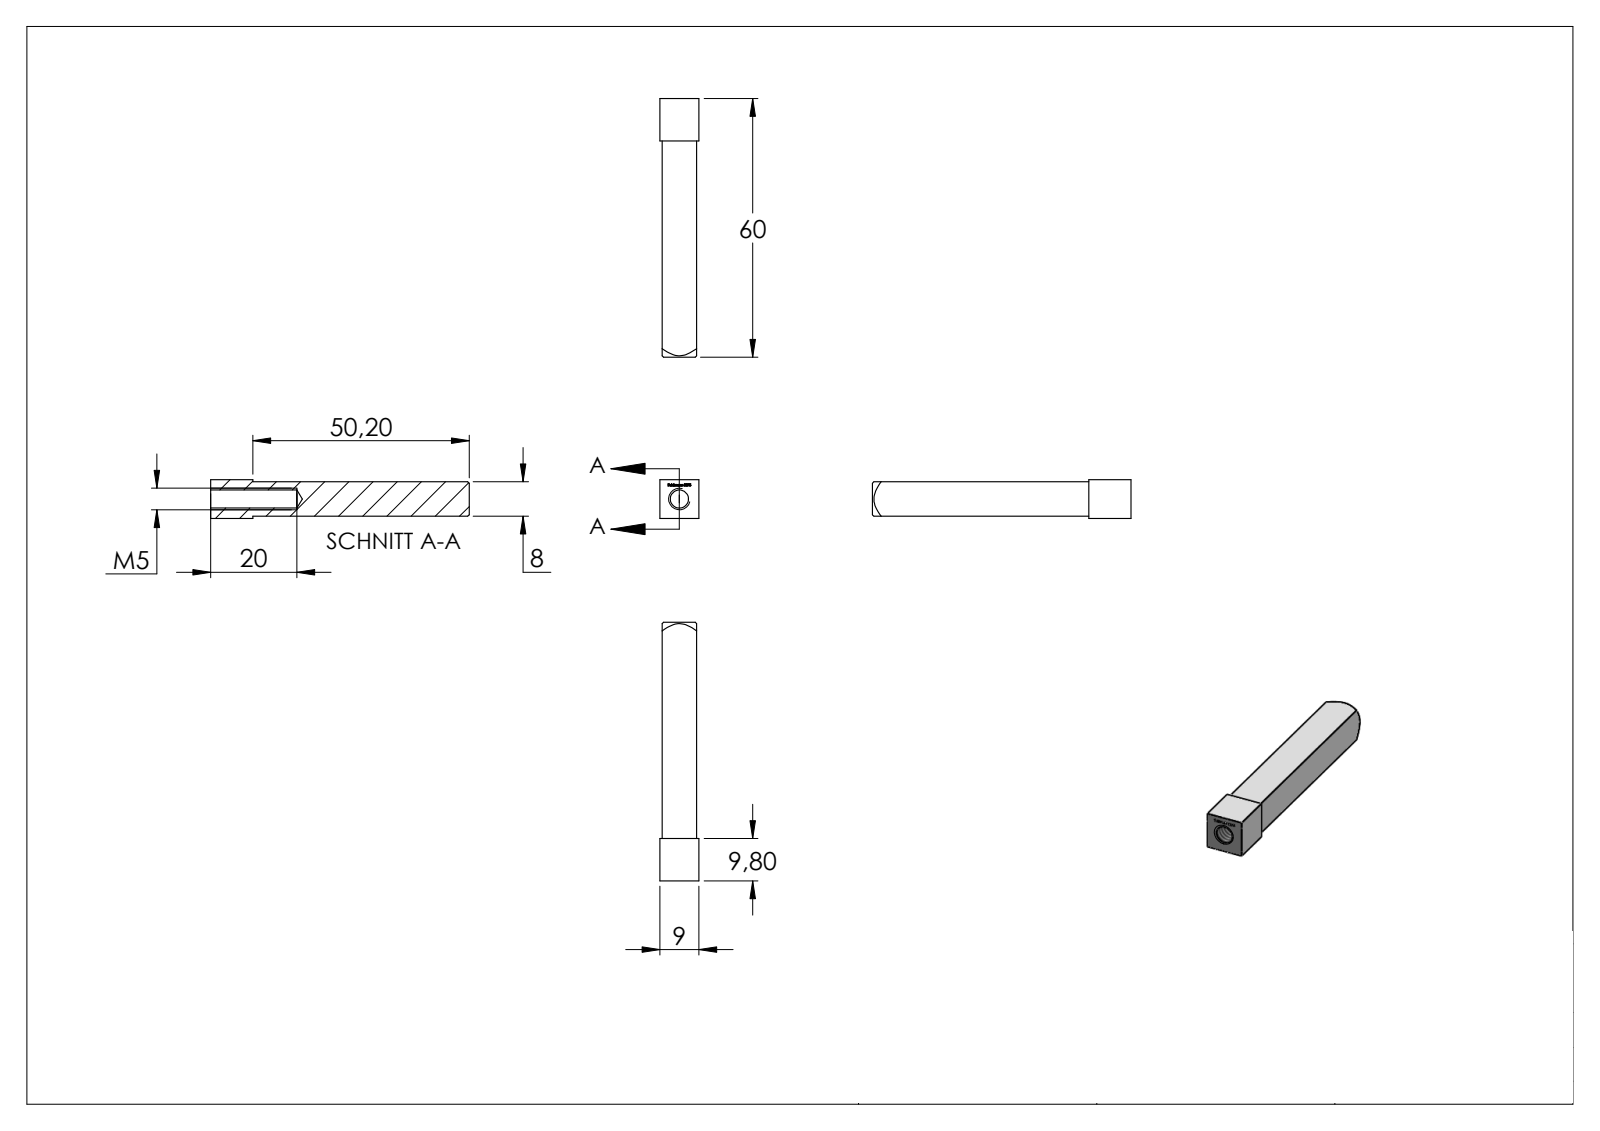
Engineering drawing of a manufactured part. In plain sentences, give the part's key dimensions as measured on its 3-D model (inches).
The part is named "8075 Teil2_8075 Teil2; 8075 Teil3; 8075 Teil1_8075 Teil1; 8075 Teil2 (+3 more)". Its 3-D file was written by "SolidWorks 2015 (CONFIG_CONTROL_DESIGN)". It is 3 solids with 201 faces: 113 planar, 3 cylindrical and 85 other. Overall it measures 4.254 by 0.354 by 0.354 inches. Its volume is 0.437 cubic inches and its surface area 9.06 square inches. Round holes: 1 of diameter 0.165, 1 of diameter 0.205. Round bosses or shafts: 1 of diameter 0.197. The main face-to-face distances are 0.315, 0.02, 0.335, 0.354, 0.022, 0.333, 0.313, 1.774, 1.892, 0.118.
